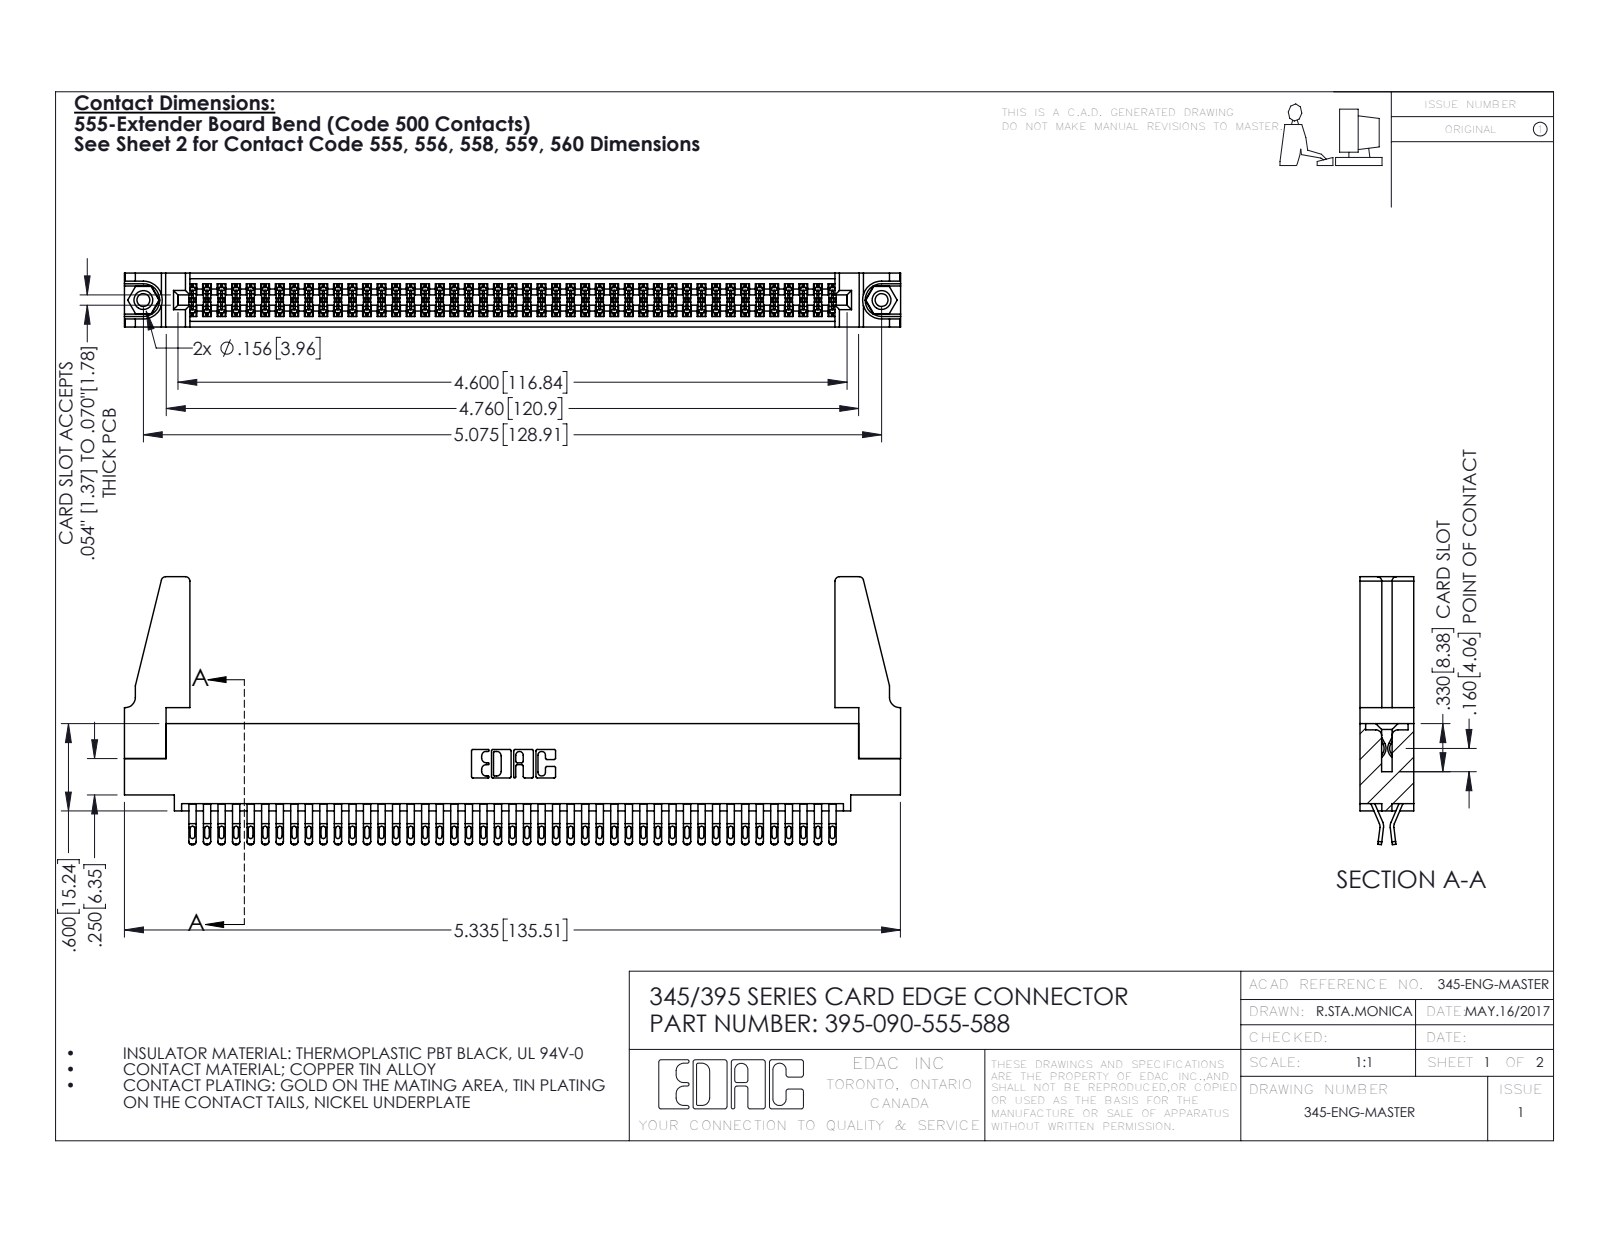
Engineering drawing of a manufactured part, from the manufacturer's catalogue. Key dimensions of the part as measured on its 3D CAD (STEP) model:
Part name (STEP PRODUCT): 395-090-555-588; 345-220-078_345-220-088; 345-292-001_555 Tail; 345 Part_0.110 Offset - 0.156 Dia-TH (+1 more)
STEP written by: SolidWorks 2016 (CONFIG_CONTROL_DESIGN)
Units: inches
Bodies: 95 solids, 5294 faces (2946 planar, 2332 cylindrical, 16 other)
Overall size (bounding box): 5.336 × 1.842 × 0.37
Volume: 1.015 in³ · Surface area: 37.14 in²
Round holes (diameter × count): ⌀0.089 ×2, ⌀0.125 ×2, ⌀0.156 ×2, ⌀0.064 ×1
Round bosses / shafts (diameter × count): ⌀0.155 ×2
Partial cylindrical surfaces — rounded edges, fillets, slot ends (radius × count): R0.016 ×225, R0.02 ×180, R0.006 ×135, R0.01 ×22, R0.03 ×8, R0.007 ×6, R0.031 ×6, R0.026 ×3
Main face-to-face distances: 0.072, 0.298, 0.37, 0.025, 0.2, 0.098, 0.272, 0.225, 0.175, 0.149
Hole centre spacings: 0.27, 4.839, 5.075
